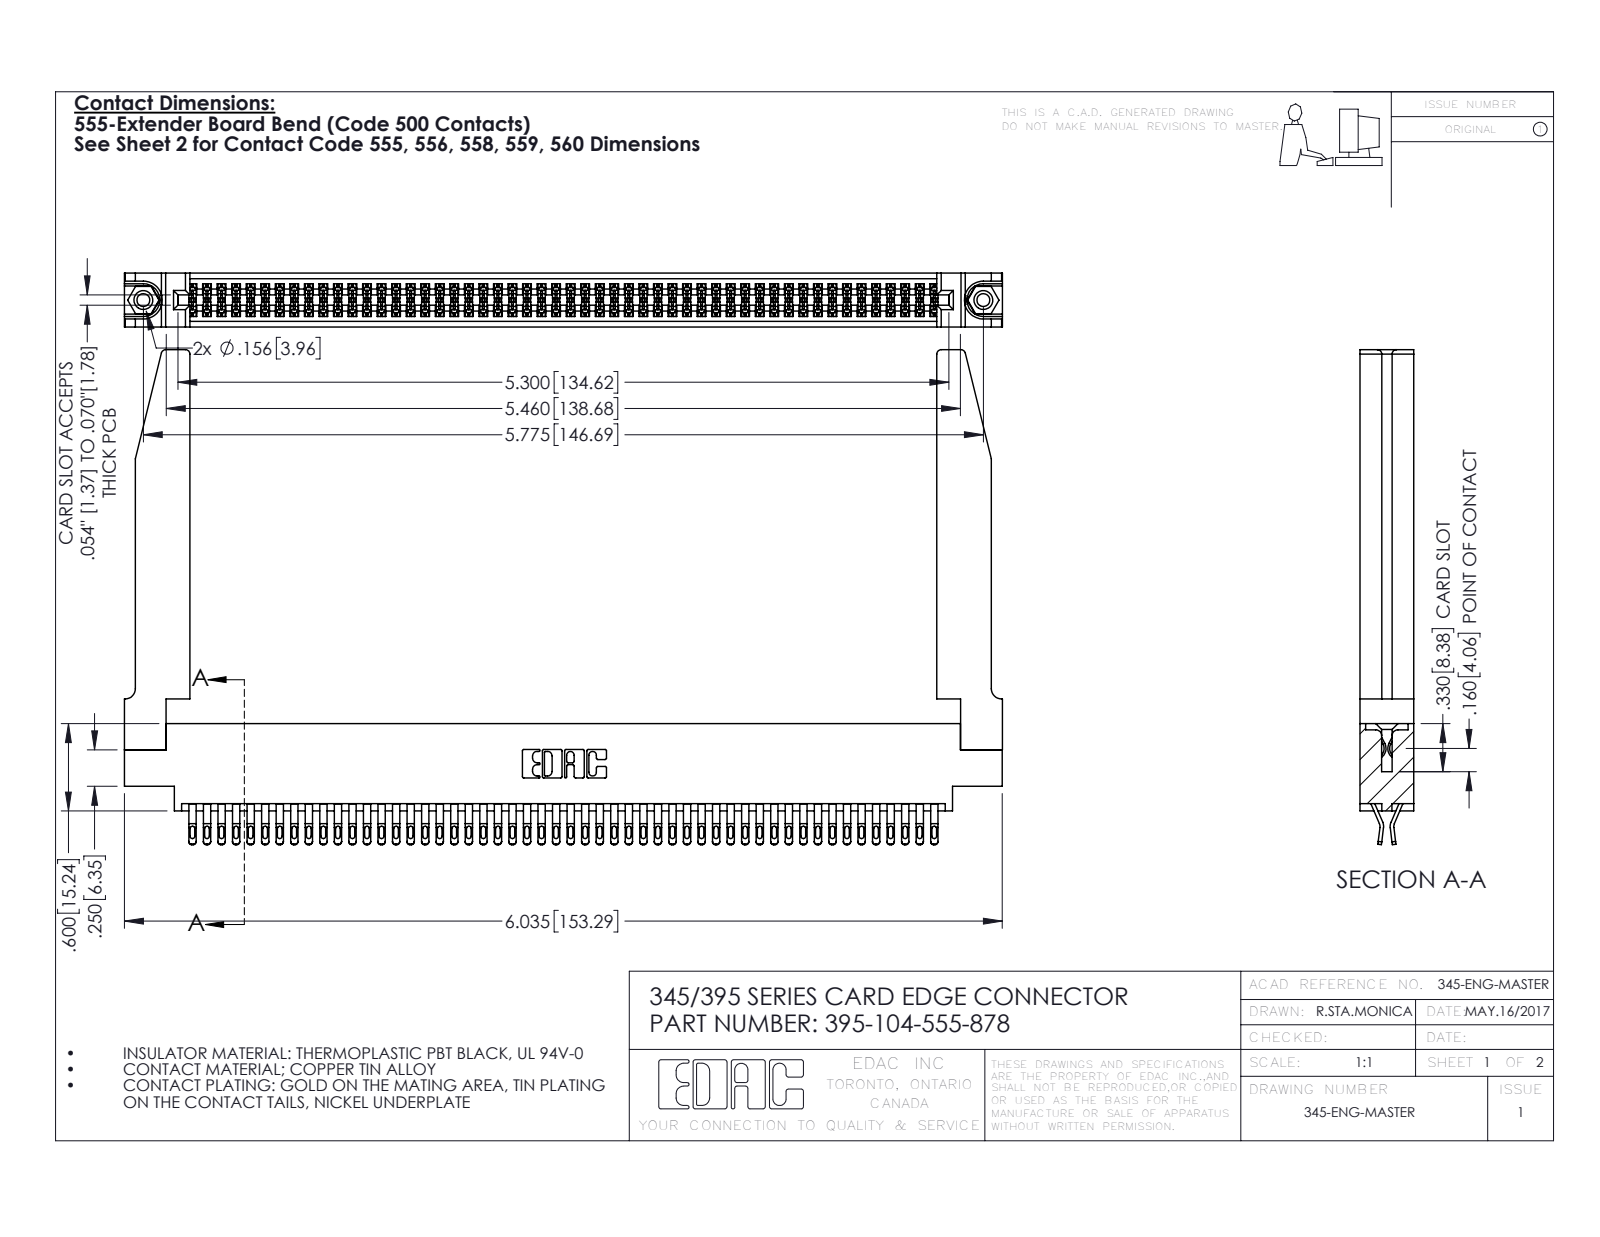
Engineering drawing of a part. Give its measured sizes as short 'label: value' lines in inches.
name: 345-250-001_345-250-001-102; 345 Part_0.170 Offset - 0.156 Dia-TH; 345-292-001_555 Tail; 345-220-078_345-220-078 (+1 more)
written by: SolidWorks 2016 (CONFIG_CONTROL_DESIGN)
unit: in
bodies: 109 solids, 6188 faces (3450 planar, 2686 cylindrical, 52 other)
size: 6.036 × 3.402 × 0.37
volume: 1.4 in³; area: 47.52 in²
holes: 2× ⌀0.089, 2× ⌀0.125, 2× ⌀0.156, 1× ⌀0.064
bosses: 2× ⌀0.155
rounds: 260× R0.016, 208× R0.02, 156× R0.006, 22× R0.01, 8× R0.03, 6× R0.007, 6× R0.031, 3× R0.026
face distances: 0.37, 0.072, 0.298, 0.025, 0.098, 0.272, 0.2, 0.225, 0.175, 0.15
hole spacings: 0.27, 5.539, 5.775
